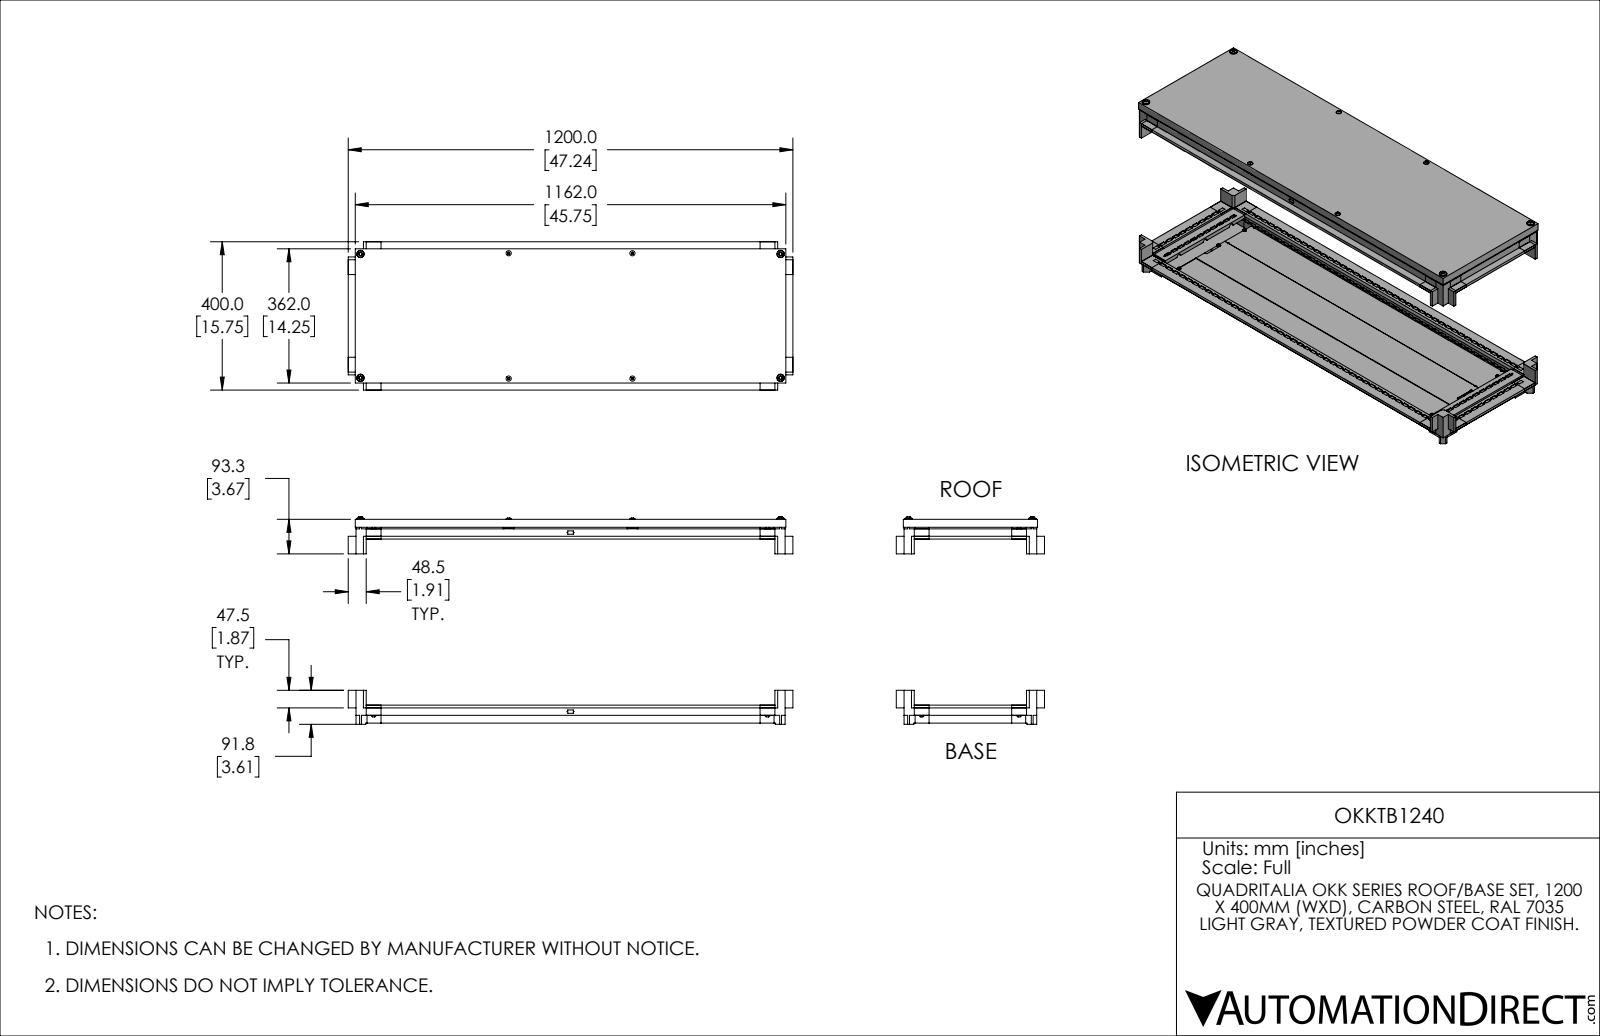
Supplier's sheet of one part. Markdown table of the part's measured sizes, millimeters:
| quantity | value |
| --- | --- |
| part name | OKKTB1240 |
| STEP written by | SolidWorks 2021 (AUTOMOTIVE_DESIGN) |
| units | millimeters |
| bodies | 75 solids, 5539 faces (4234 planar, 1086 cylindrical, 219 other) |
| overall size | 1200 × 559.1 × 400 |
| volume | 8 875 000 mm³ |
| surface area | 3 377 000 mm² |
| round holes (diameter × count) | 4.2 × 252, 9 × 15, 0.3 × 12, 3.9 × 8, 4.9 × 4, 7.5 × 4, 13.5 × 4, 4.9 × 3, 8.2 × 3 |
| round bosses / shafts (diameter × count) | 14 × 15, 8 × 11, 10 × 9, 6 × 8, 5 × 6, 20 × 4, 12 × 4, 7 × 1 |
| partial cylindrical surfaces (radius × count) | 0.5 × 312, 1 × 24, 0.2 × 16, 0.3 × 16, 4.5 × 12, 3.5 × 8, 5.5 × 6, 2 × 4 |
| main face-to-face distances | 1.5, 526.1, 527.6, 20, 27.5, 7.5, 524.6, 20.5, 28, 2.5 |
| hole center spacings | 25, 50, 75, 100, 125, 150, 175, 200 |
